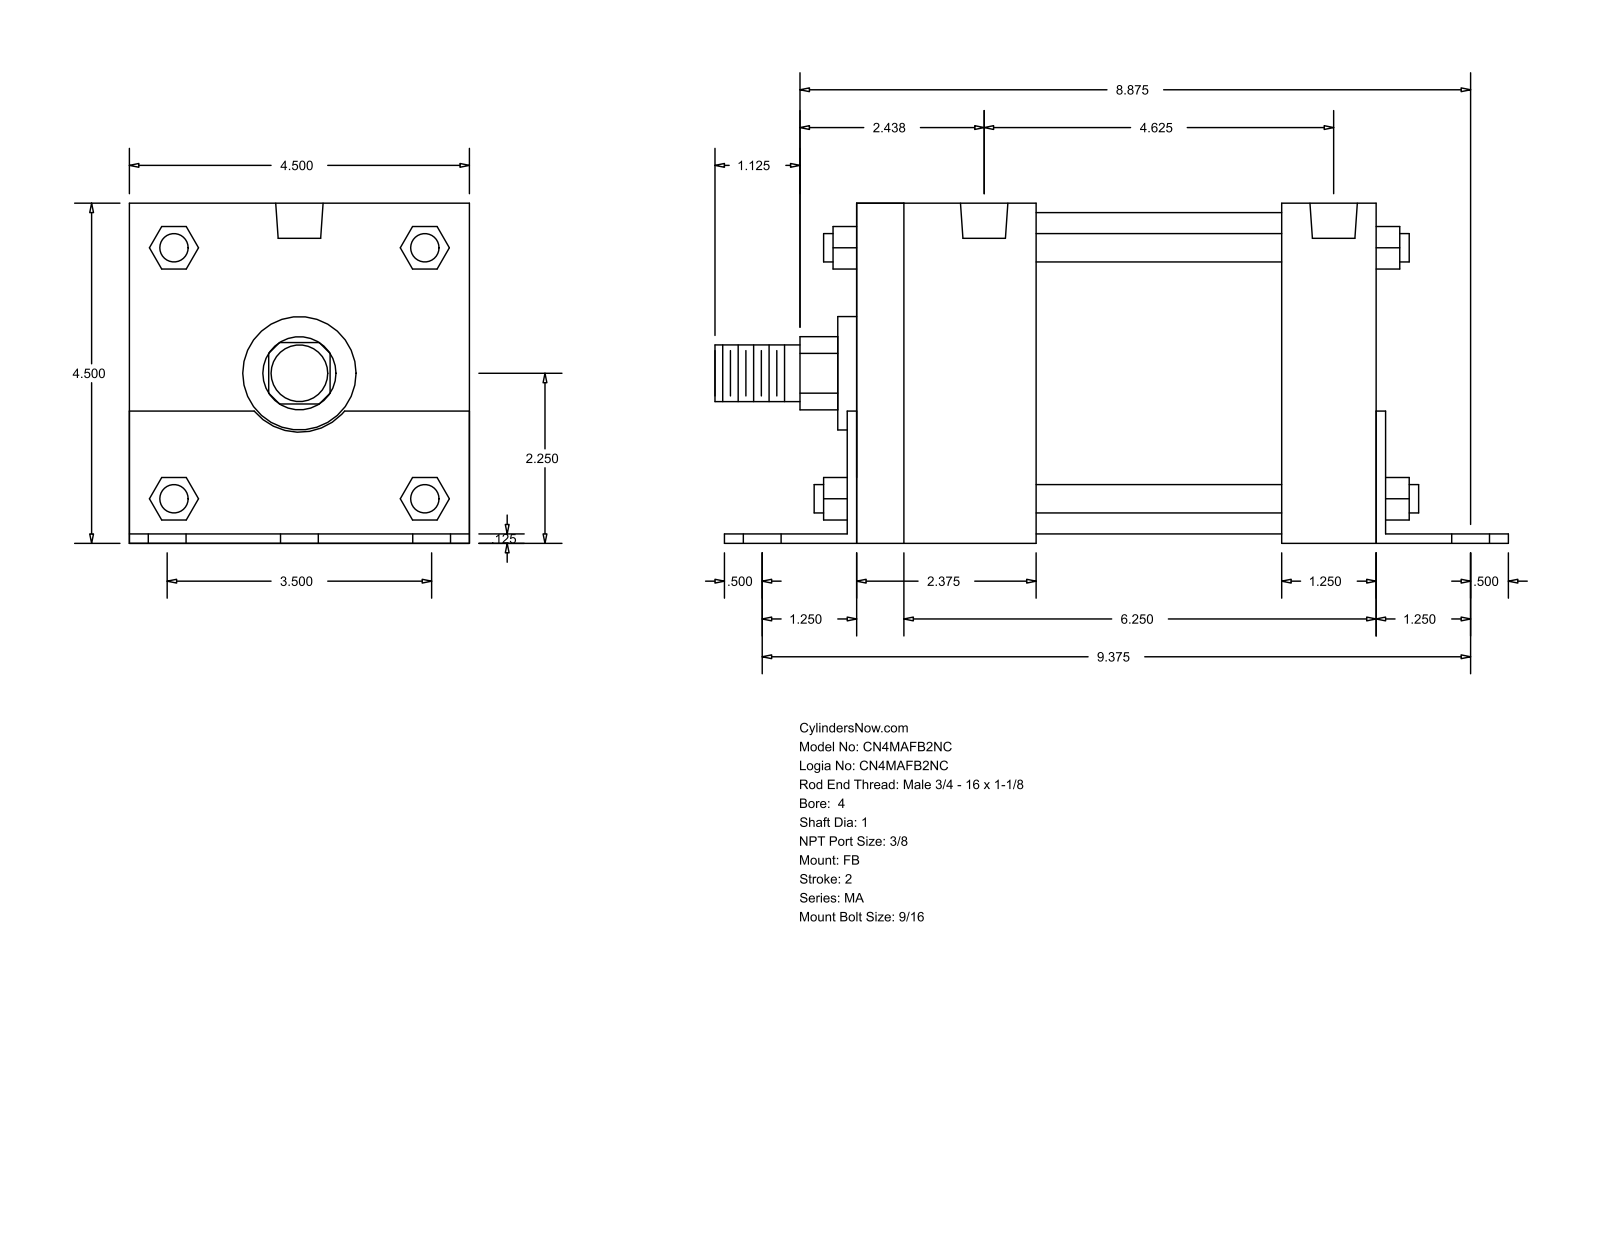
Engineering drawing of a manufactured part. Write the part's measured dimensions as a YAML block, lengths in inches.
part_name: "MA_FB__0400_1"
step_written_by: "GSSL Pune (CONFIG_CONTROL_DESIGN)"
units: inches
bodies: {solids: 0, faces: 140, planar: 105, cylindrical: 35, other: 0}
overall_size: [10.5, 4.502, 4.5]
round_holes:
  - {diameter: 0.563, count: 6}
  - {diameter: 0.437, count: 4}
  - {diameter: 0.627, count: 2}
round_bosses_or_shafts:
  - {diameter: 0.375, count: 4}
  - {diameter: 4.25, count: 1}
  - {diameter: 1.5, count: 1}
  - {diameter: 1, count: 1}
  - {diameter: 0.75, count: 1}
partial_cylinders:
  - {radius: 0.484, count: 1}
  - {radius: 0.78, count: 1}
face_to_face_distances: [4.5, 0.125, 4.502, 7, 0.123, 4.377, 6.875, 7.125, 5.75, 5.625]
hole_center_spacings: [1.75, 9.537, 9.375, 2.52, 2.658, 3.419, 3.5, 3.581]
